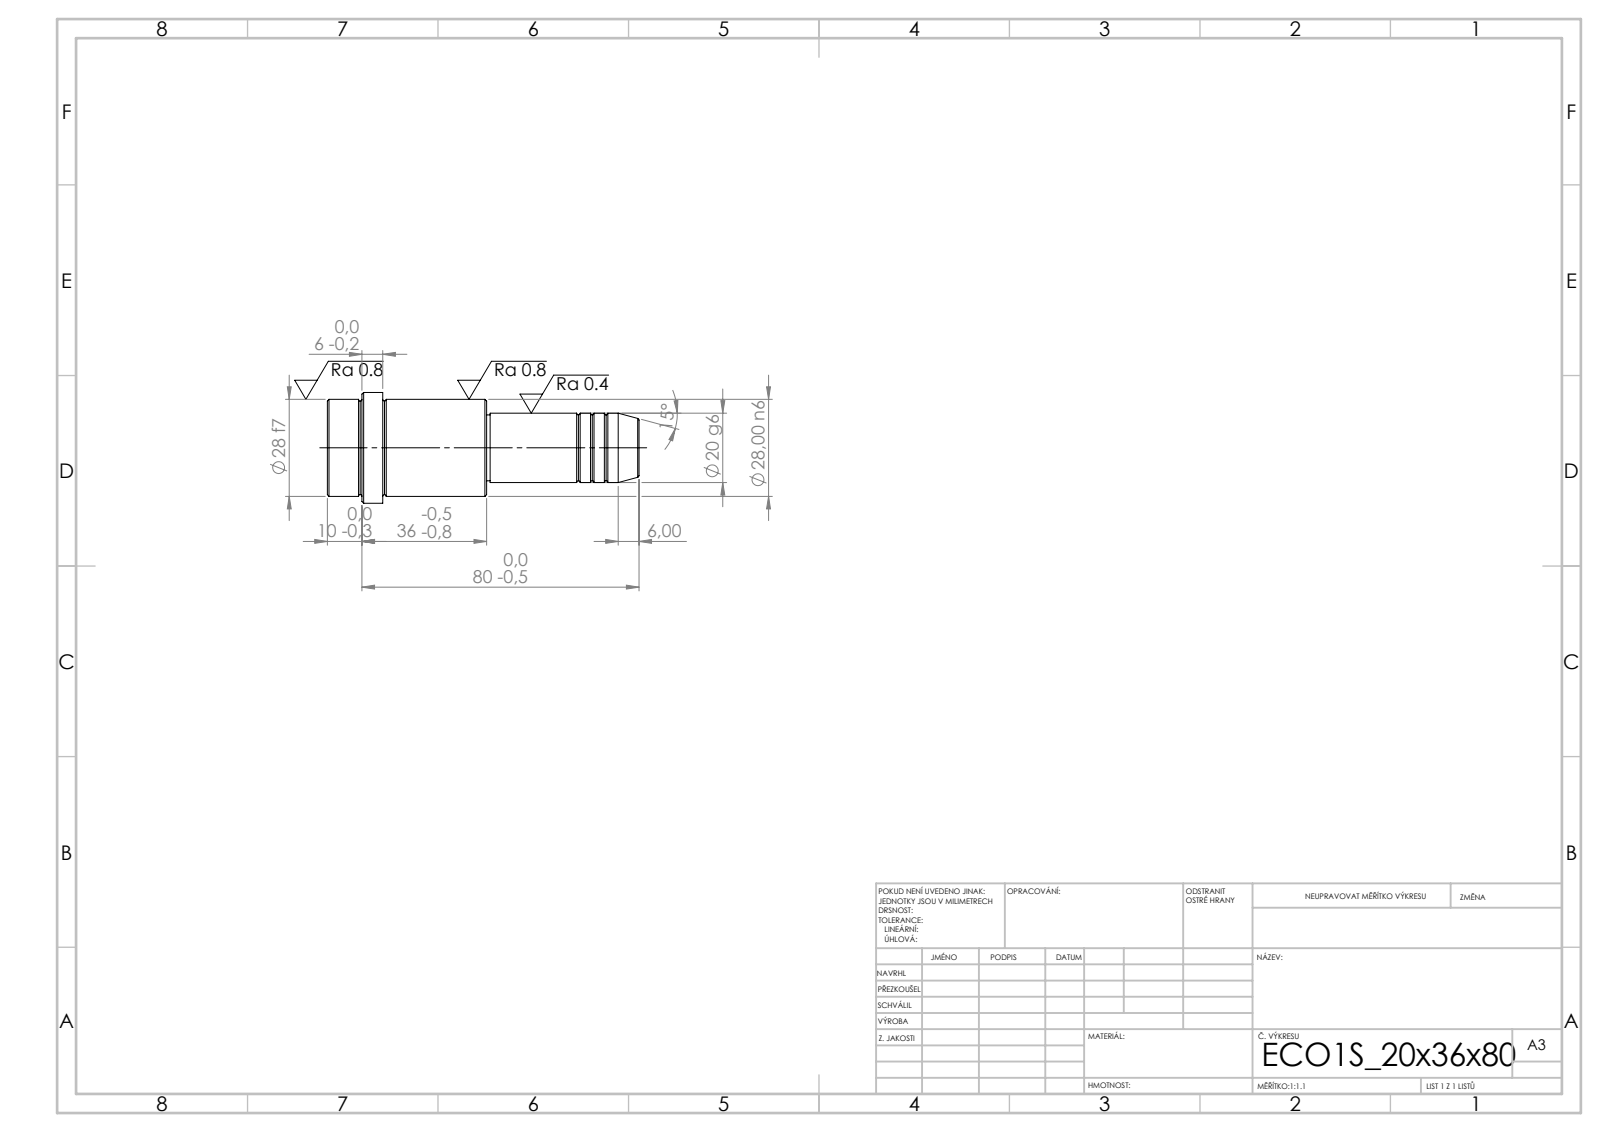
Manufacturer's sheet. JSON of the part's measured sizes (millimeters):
{"step_written_by": "SolidWorks 2019 (CONFIG_CONTROL_DESIGN)", "units": "millimeters", "bodies": {"solids": 1, "faces": 52, "planar": 6, "cylindrical": 16, "other": 30}, "overall_size": [90, 32, 32], "volume_mm3": 42785, "surface_area_mm2": 8546, "round_bosses_or_shafts": [[32, 1], [28, 1], [20, 1], [19, 1]], "face_to_face_distances": [46, 44, 90, 74, 30, 16, 80, 36, 6, 10]}
